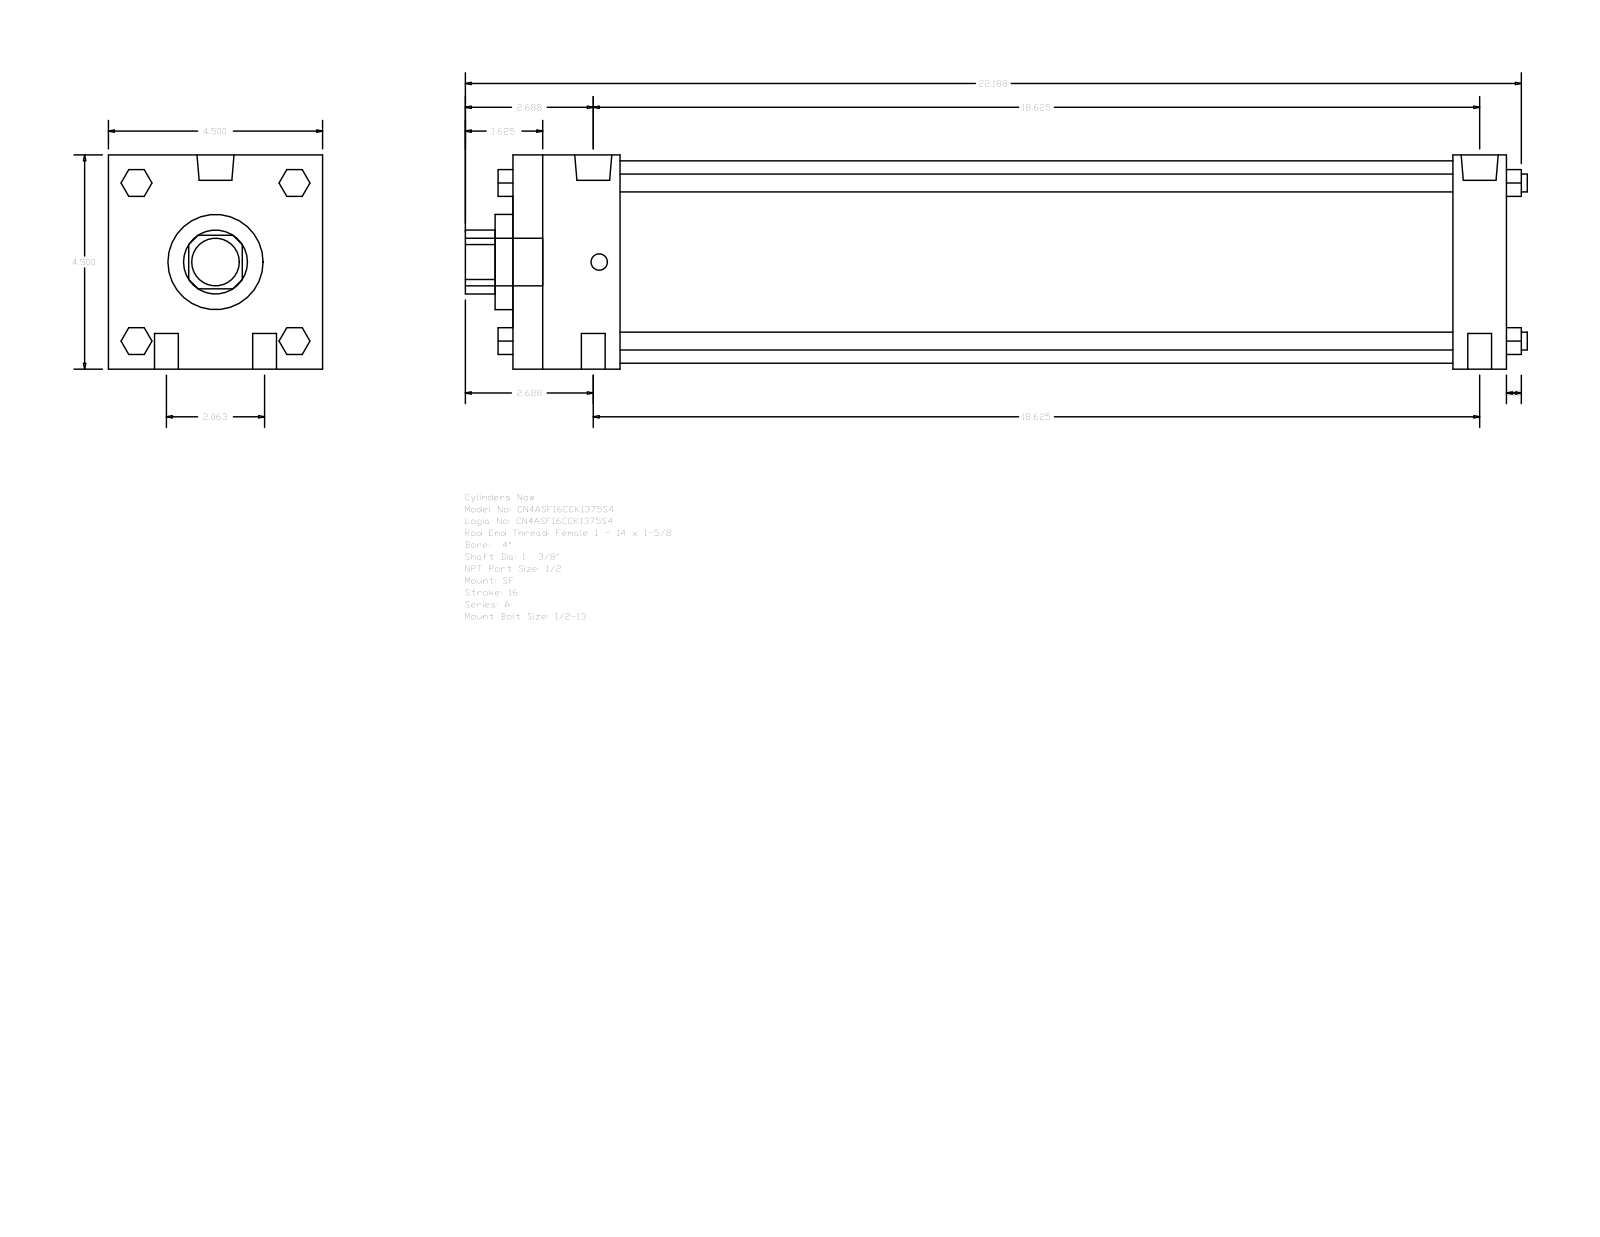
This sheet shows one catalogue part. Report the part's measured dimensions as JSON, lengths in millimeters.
{"part_name": "A_SF__0400_1.375", "step_written_by": "GSSL Pune (CONFIG_CONTROL_DESIGN)", "units": "millimeters", "bodies": {"solids": 0, "faces": 124, "planar": 94, "cylindrical": 30, "other": 0}, "overall_size": [566.74, 114.3, 114.3], "round_holes": [[34.92, 1], [50.8, 1], [107.95, 1]], "round_bosses_or_shafts": [[12.7, 4], [9.53, 4], [19.77, 2], [8.73, 2], [25.4, 1]], "partial_cylinders_radius": [[17.06, 1]], "face_to_face_distances": [114.3, 530.22, 28.57, 501.65, 57.15, 444.5, 473.07, 14.29, 9.52, 66.67]}
